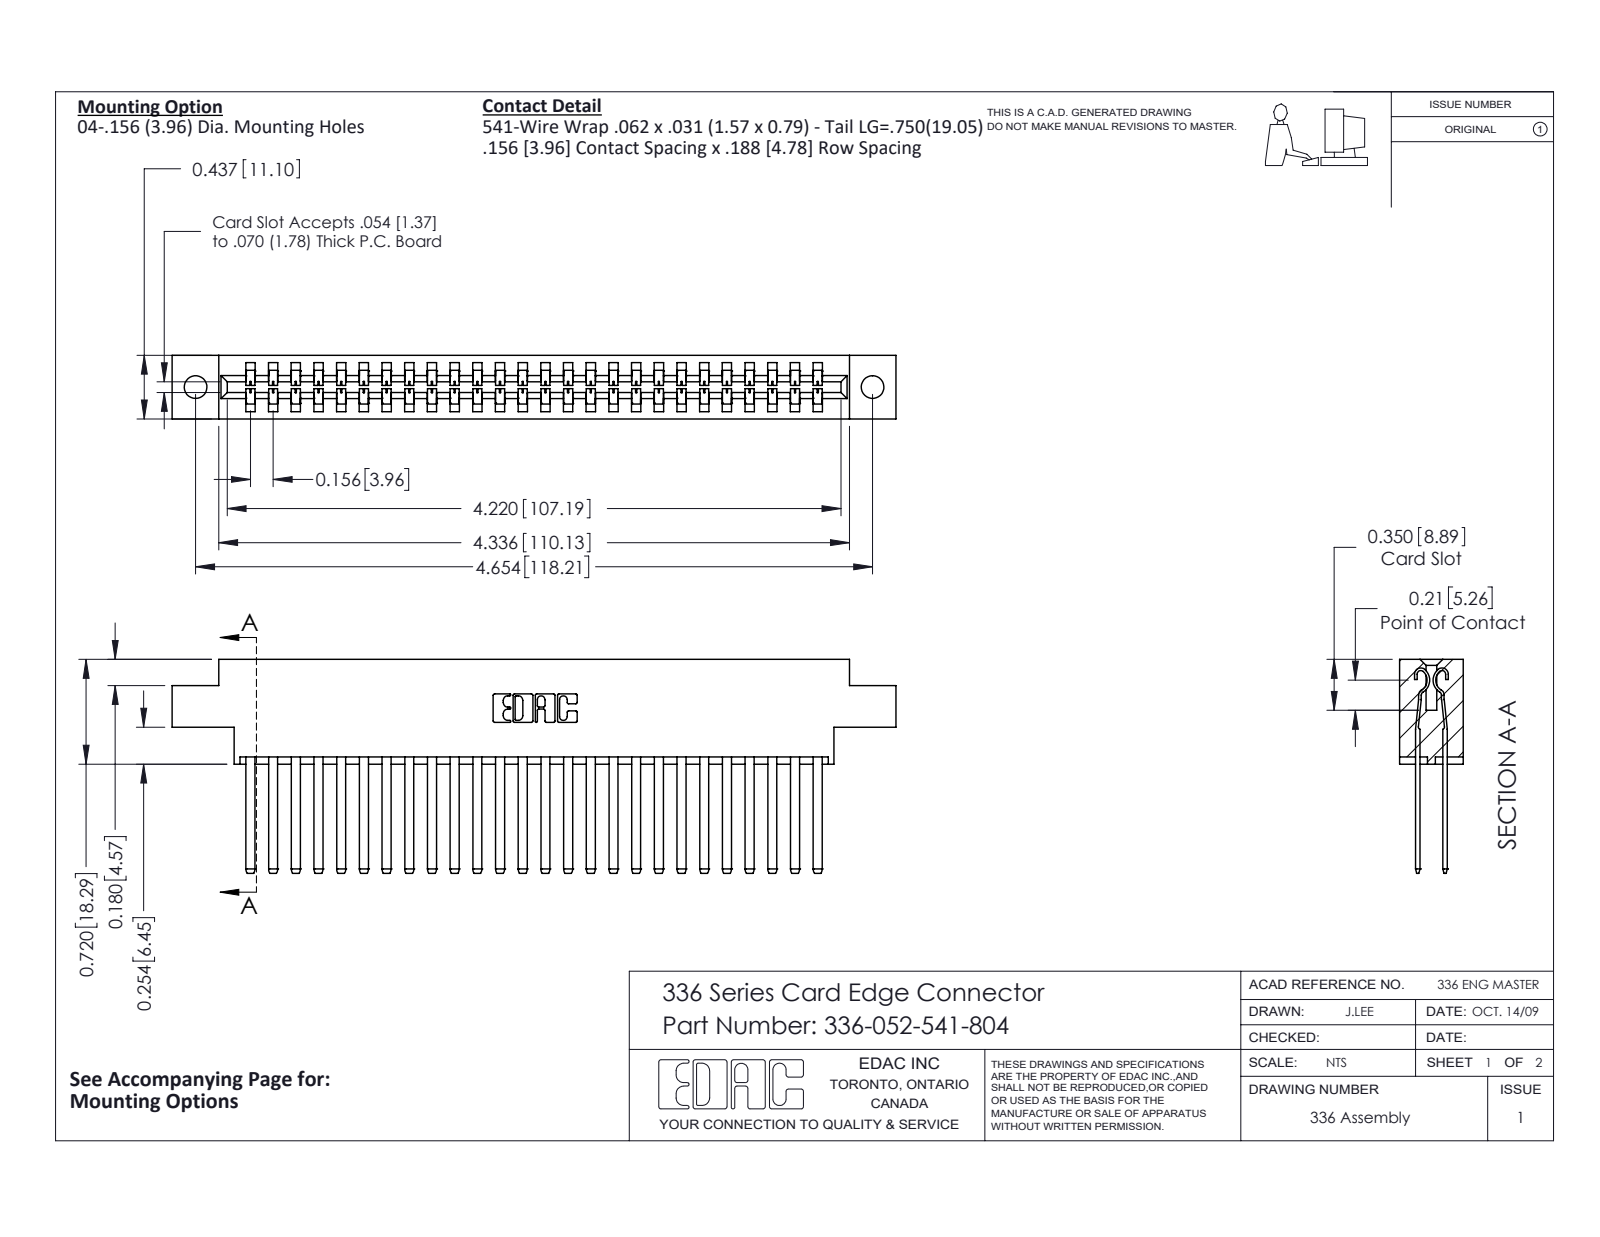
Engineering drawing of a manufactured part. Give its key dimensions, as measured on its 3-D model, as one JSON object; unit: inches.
{"part_name": "336-052-541-804; 336-290-001_336-290-541; 336 Part_Offset - .156 Dia - TH", "step_written_by": "SolidWorks 2020 (CONFIG_CONTROL_DESIGN)", "units": "inches", "bodies": {"solids": 53, "faces": 2302, "planar": 1426, "cylindrical": 876, "other": 0}, "overall_size": [4.977, 1.47, 0.437], "volume_in3": 1.155, "surface_area_in2": 36.86, "round_holes": [[0.156, 2]], "partial_cylinders_radius": [[0.004, 104], [0.056, 52], [0.01, 22], [0.007, 6], [0.031, 6], [0.022, 4], [0.04, 4], [0.026, 3]], "face_to_face_distances": [0.188, 0.328, 0.14, 0.297, 0.109, 0.031, 0.437, 0.033, 0.181, 0.256], "hole_center_spacings": [4.654]}
